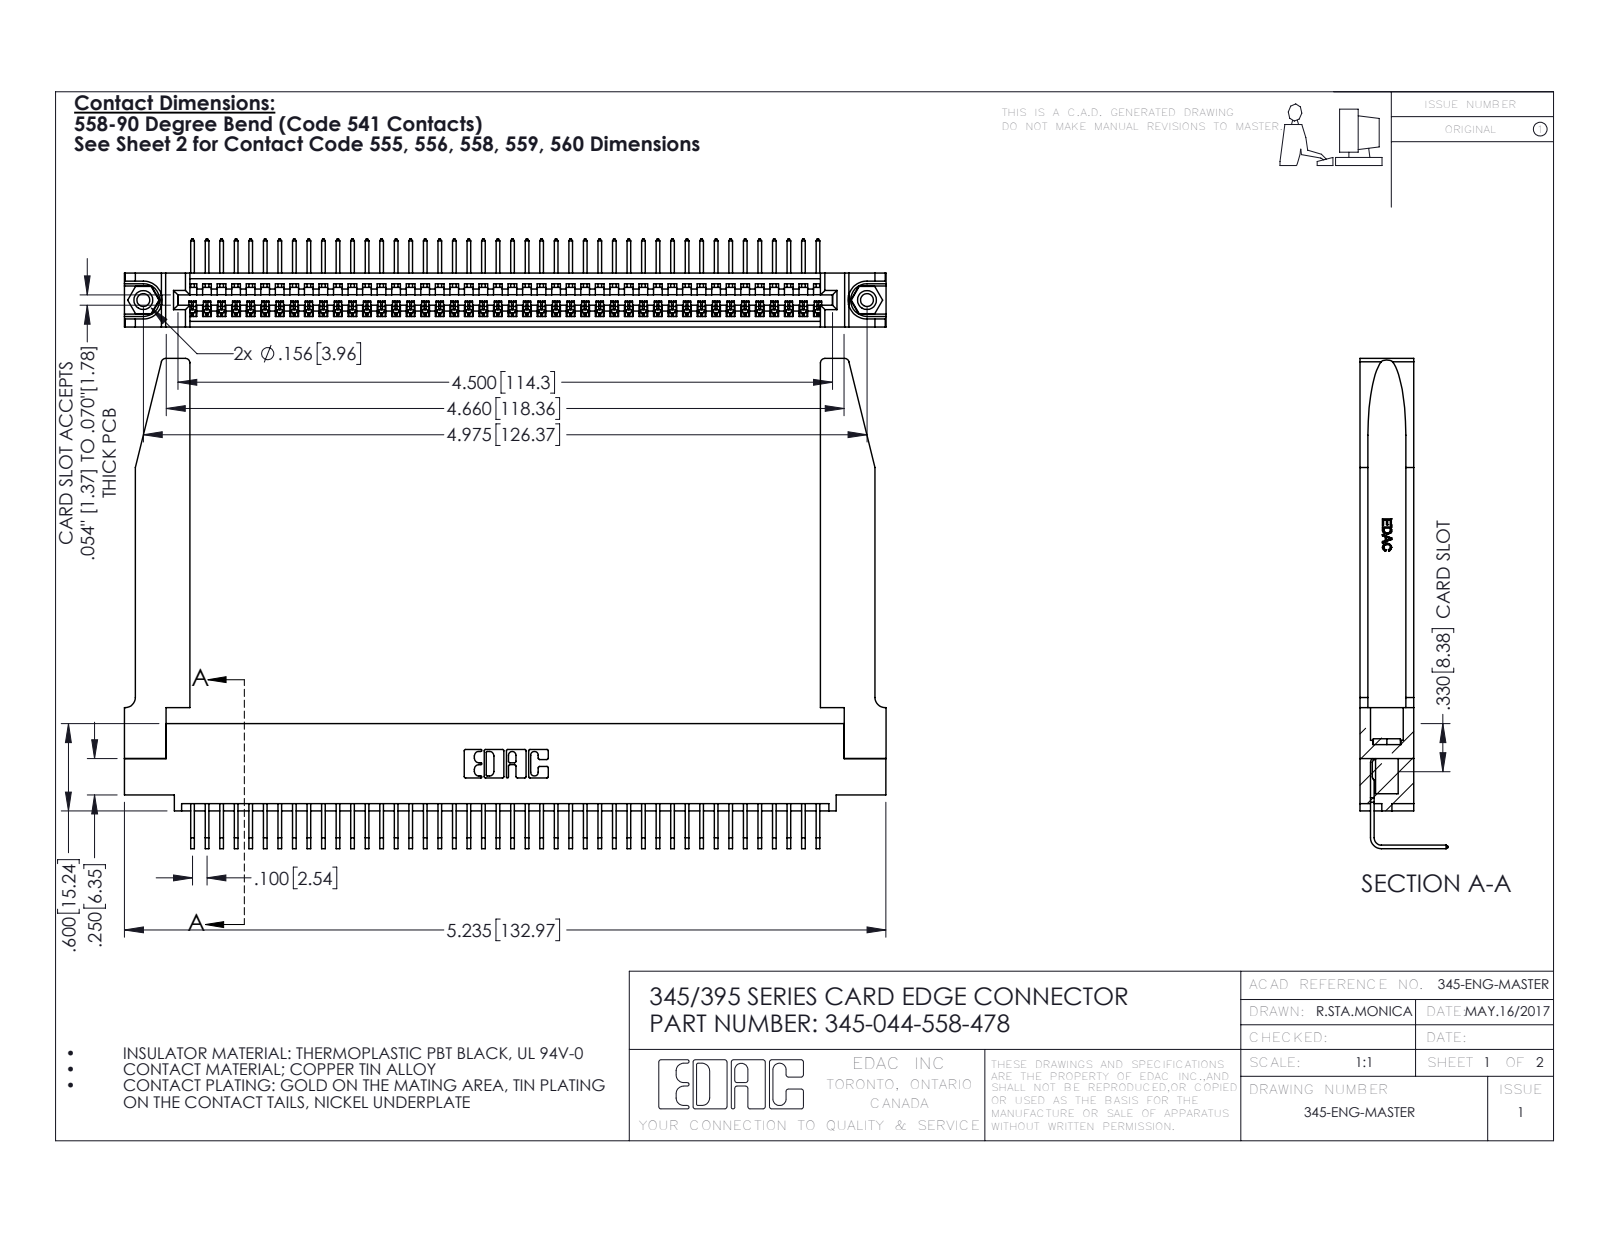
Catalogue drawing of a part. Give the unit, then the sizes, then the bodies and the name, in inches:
Units: inches
Overall size (bounding box): 5.236 × 3.369 × 0.605
Round holes (diameter × count): ⌀0.089 ×2, ⌀0.125 ×2, ⌀0.156 ×2, ⌀0.064 ×1
Round bosses / shafts (diameter × count): ⌀0.155 ×2
Partial cylindrical surfaces — rounded edges, fillets, slot ends (radius × count): R0.006 ×88, R0.01 ×22, R0.03 ×8, R0.007 ×6, R0.031 ×6, R0.026 ×3, R0.031 ×2, R0.04 ×2
Main face-to-face distances: 0.37, 0.072, 0.298, 0.2, 0.098, 0.272, 0.025, 0.225, 0.148, 0.15
Hole centre spacings: 0.27, 4.739, 4.975
Volume: 1.251 in³ · Surface area: 38.32 in²
Bodies: 49 solids, 3004 faces (2074 planar, 878 cylindrical, 52 other)
Part name (STEP PRODUCT): 345-292-001_558 Tail - 2; 345-044-558-478; 345-250-001_345-250-001-102; 345-220-078_345-220-078 (+1 more)
STEP written by: SolidWorks 2016 (CONFIG_CONTROL_DESIGN)
